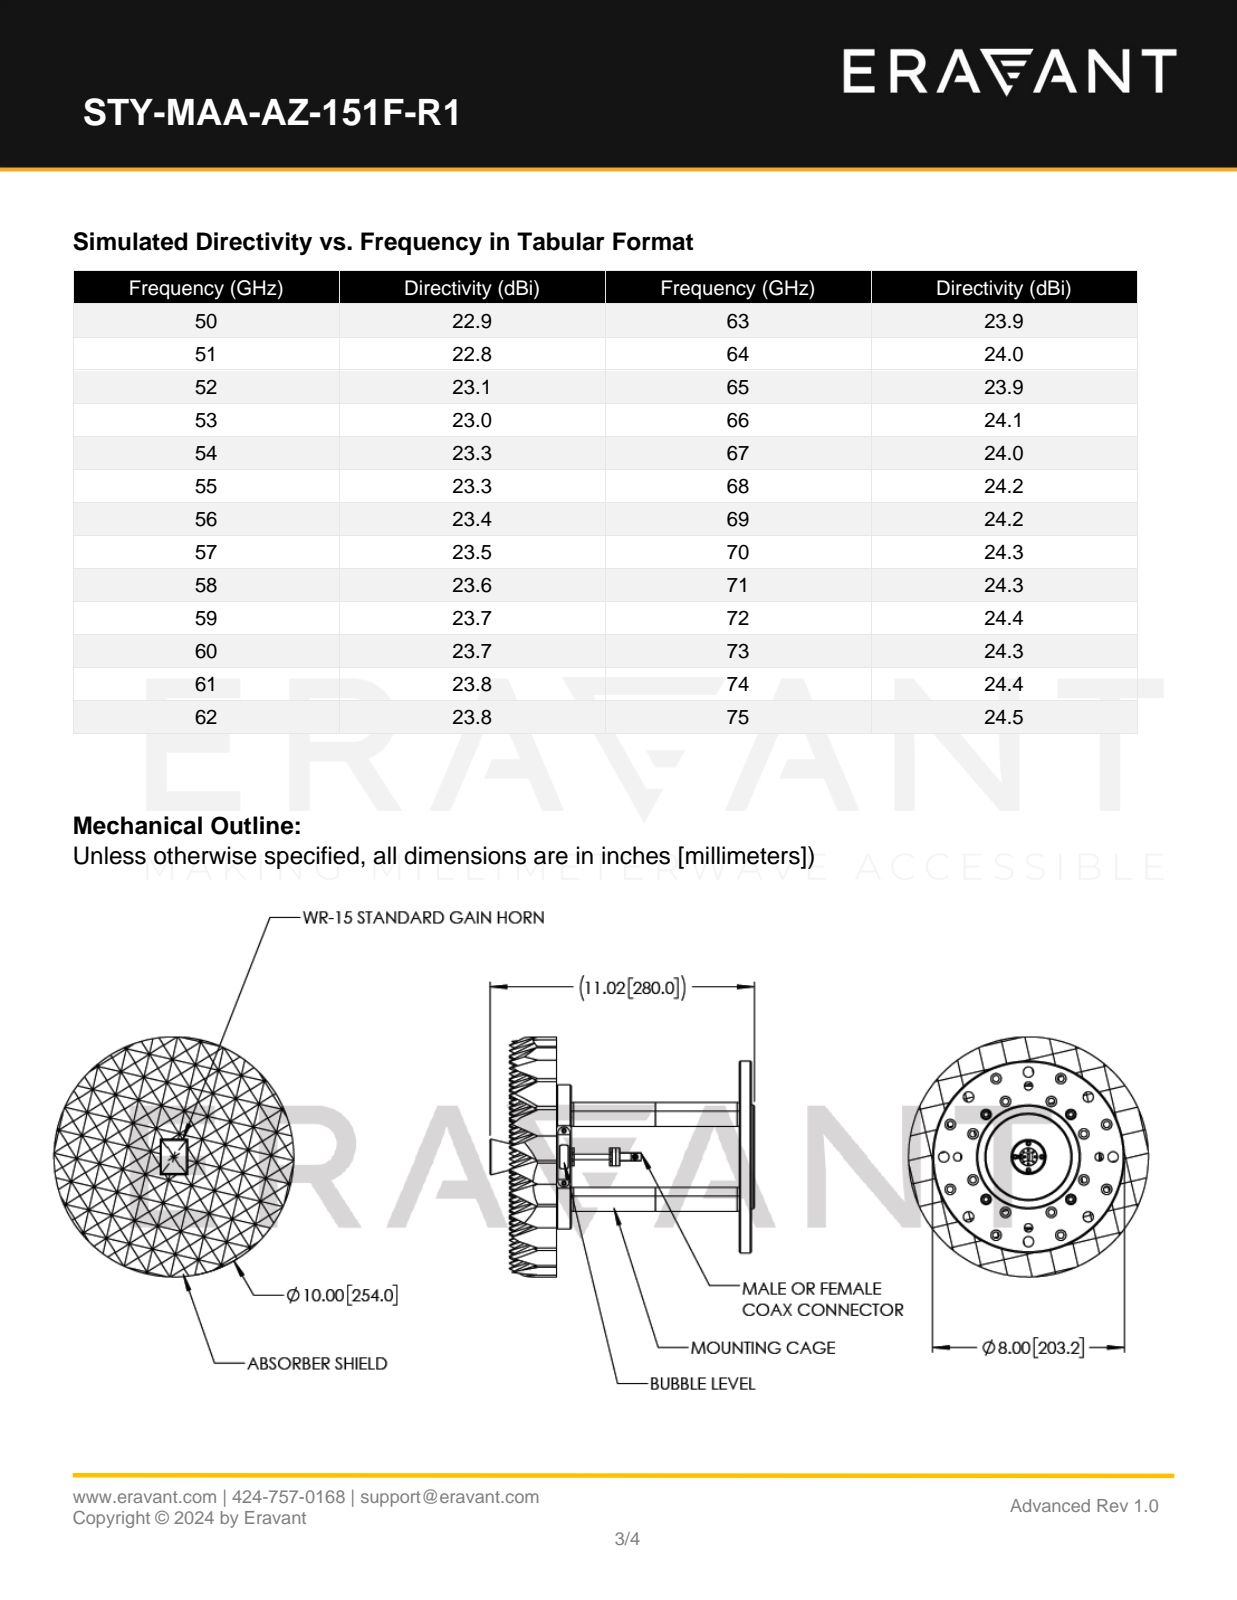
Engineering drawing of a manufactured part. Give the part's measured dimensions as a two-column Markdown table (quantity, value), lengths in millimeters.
| quantity | value |
| --- | --- |
| part name | STY-MAA-AZ-151F-R1 |
| STEP written by | SolidWorks 2021 (CONFIG_CONTROL_DESIGN) |
| units | millimeters |
| bodies | 84 solids, 1443 faces (631 planar, 338 cylindrical, 474 other) |
| overall size | 280 × 254 × 254 |
| volume | 2 504 000 mm³ |
| surface area | 493 600 mm² |
| round holes (diameter × count) | 6.8 × 20, 11.1 × 16, 11 × 8, 8.8 × 4, 19.1 × 4, 2.3 × 2, 3.2 × 2, 0.3 × 1, 1 × 1, 2.4 × 1, 35.6 × 1, 90 × 1 |
| round bosses / shafts (diameter × count) | 25.4 × 4, 11.1 × 4, 4.6 × 4, 254 × 1, 203.2 × 1, 152.4 × 1, 110 × 1, 19.1 × 1 |
| partial cylindrical surfaces (radius × count) | 0.1 × 48, 2 × 2, 6.4 × 2, 6.1 × 1 |
| main face-to-face distances | 25, 50, 25, 50, 75, 100, 100, 75, 150, 125 |
| hole center spacings | 109.9, 141.9, 87.8, 128.2, 150.3, 39.4, 63.4, 89.7 |
